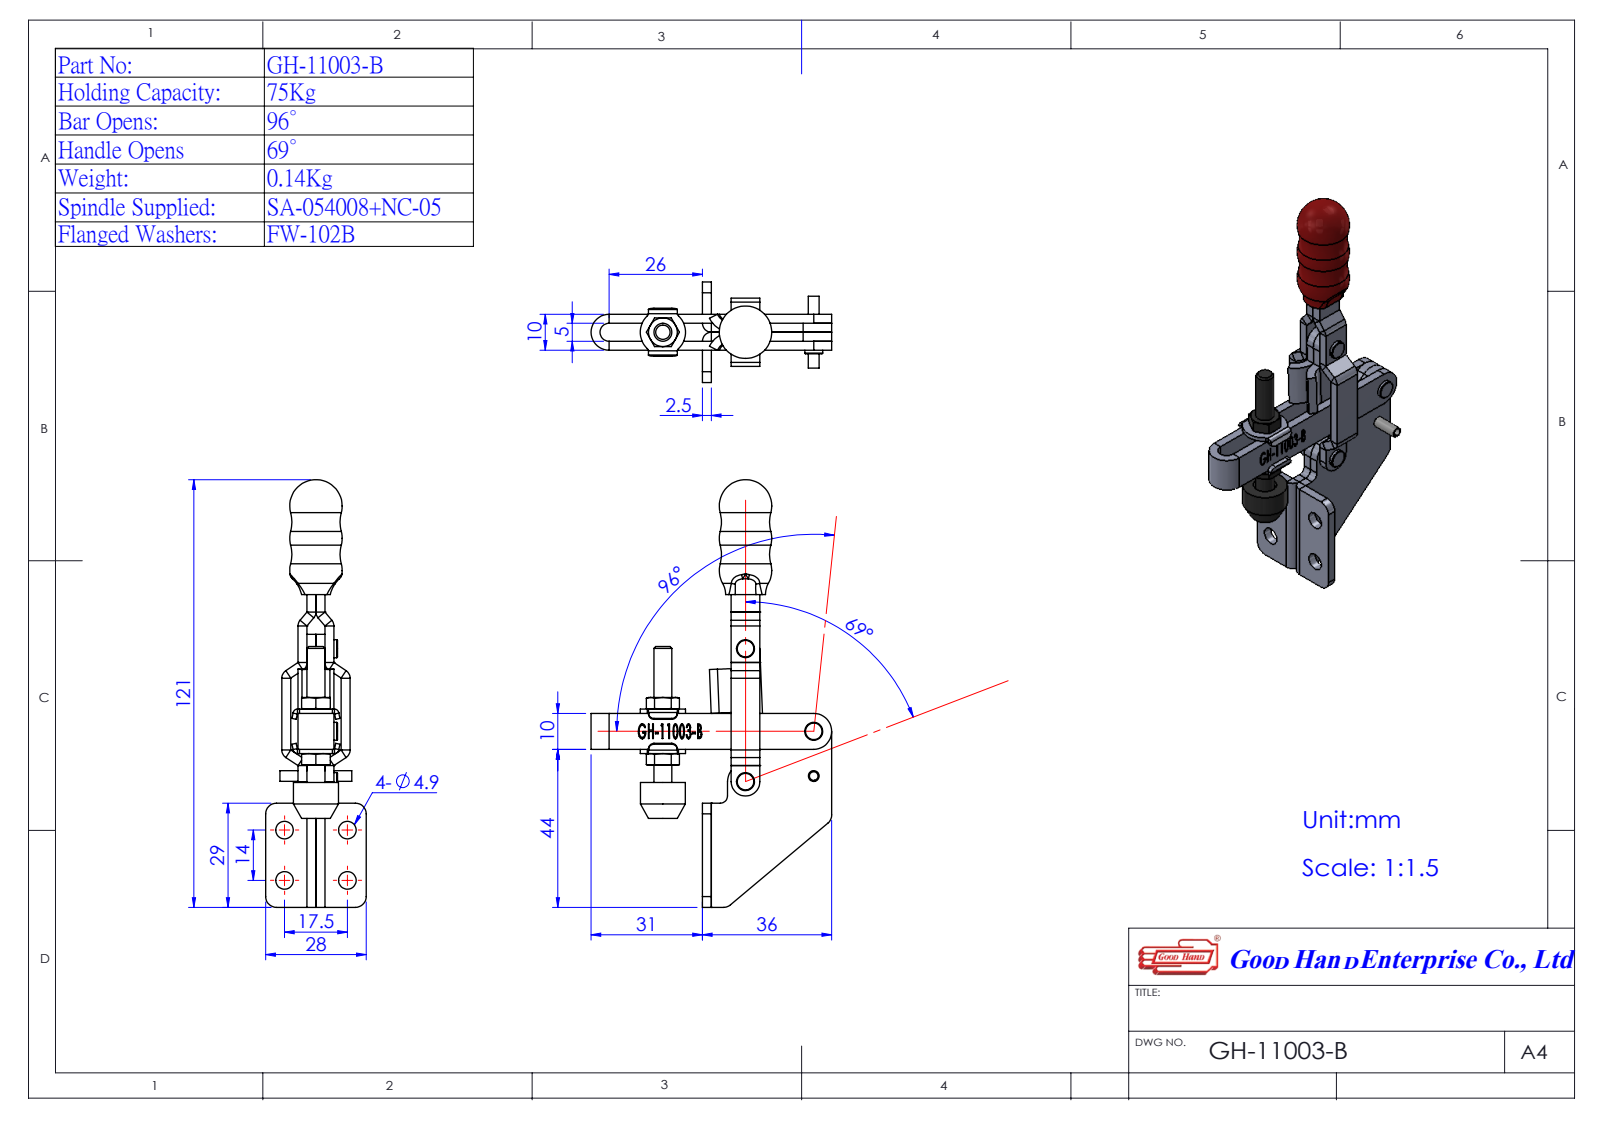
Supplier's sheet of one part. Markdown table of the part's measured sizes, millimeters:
| quantity | value |
| --- | --- |
| part name | Group2^GH-11003-B(簡化)-1; Group3^GH-11003-B(簡化)-1; Group1^GH-11003-B(簡化)-1; Group5^GH-11003-B(簡化)-1 (+2 more) |
| STEP written by | SolidWorks 2016 (AUTOMOTIVE_DESIGN) |
| units | millimeters |
| bodies | 6 solids, 274 faces (126 planar, 96 cylindrical, 52 other) |
| overall size | 118.98 × 67 × 28 |
| volume | 21 868 mm³ |
| surface area | 16 032 mm² |
| round holes (diameter × count) | 2.5 × 4, 4.8 × 4 |
| round bosses / shafts (diameter × count) | 5 × 5, 12.5 × 1, 3 × 1 |
| partial cylindrical surfaces (radius × count) | 0.5 × 4, 1 × 4, 2.2 × 4, 3 × 4, 4 × 3, 4.5 × 2, 5 × 2, 7 × 2 |
| main face-to-face distances | 2.5, 5, 7.5, 10, 8, 4.5, 7, 12, 9.5, 16.5 |
| hole center spacings | 14, 17.5, 22.41, 14.02, 18.25, 23.01, 23.6, 29.83 |
